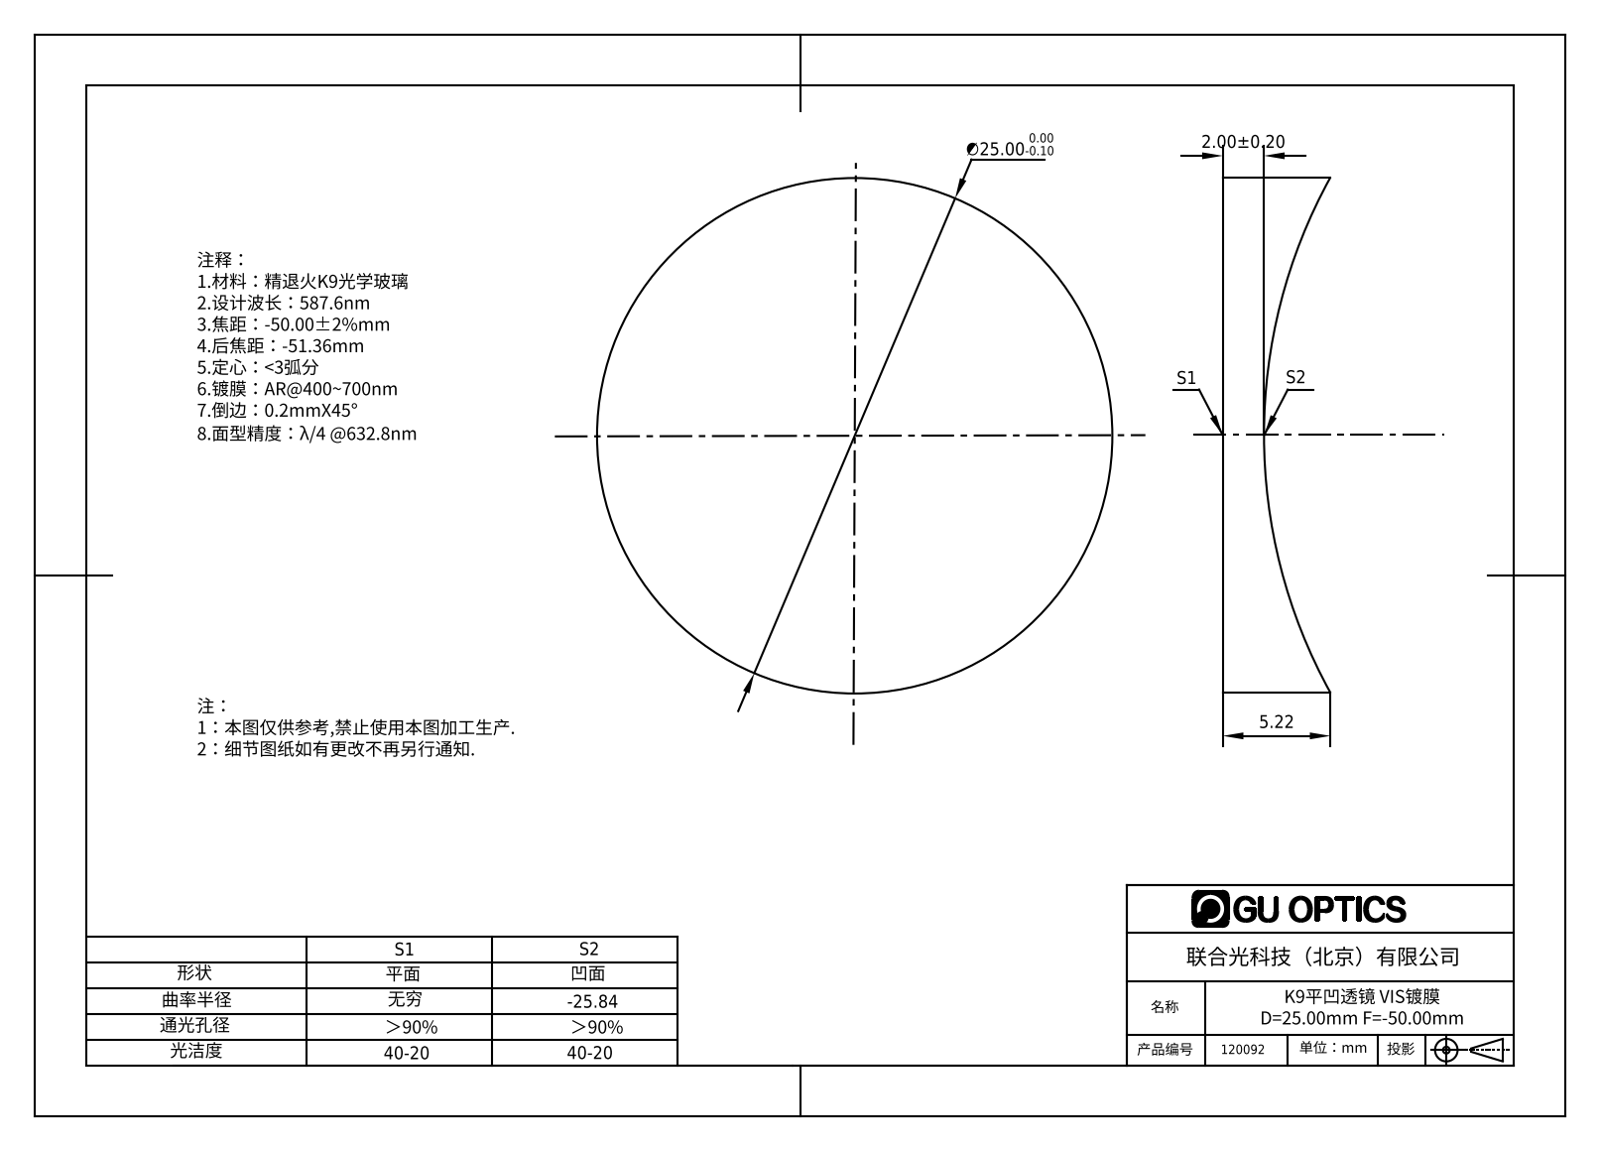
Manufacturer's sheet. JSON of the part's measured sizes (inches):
{"part_name": "120032", "step_written_by": "SolidWorks 2016 (AUTOMOTIVE_DESIGN)", "units": "inches", "bodies": {"solids": 1, "faces": 5, "planar": 1, "cylindrical": 2, "other": 2}, "overall_size": [0.984, 0.984, 0.206], "volume_in3": 0.107, "surface_area_in2": 2.209, "round_bosses_or_shafts": [[0.984, 1]]}
